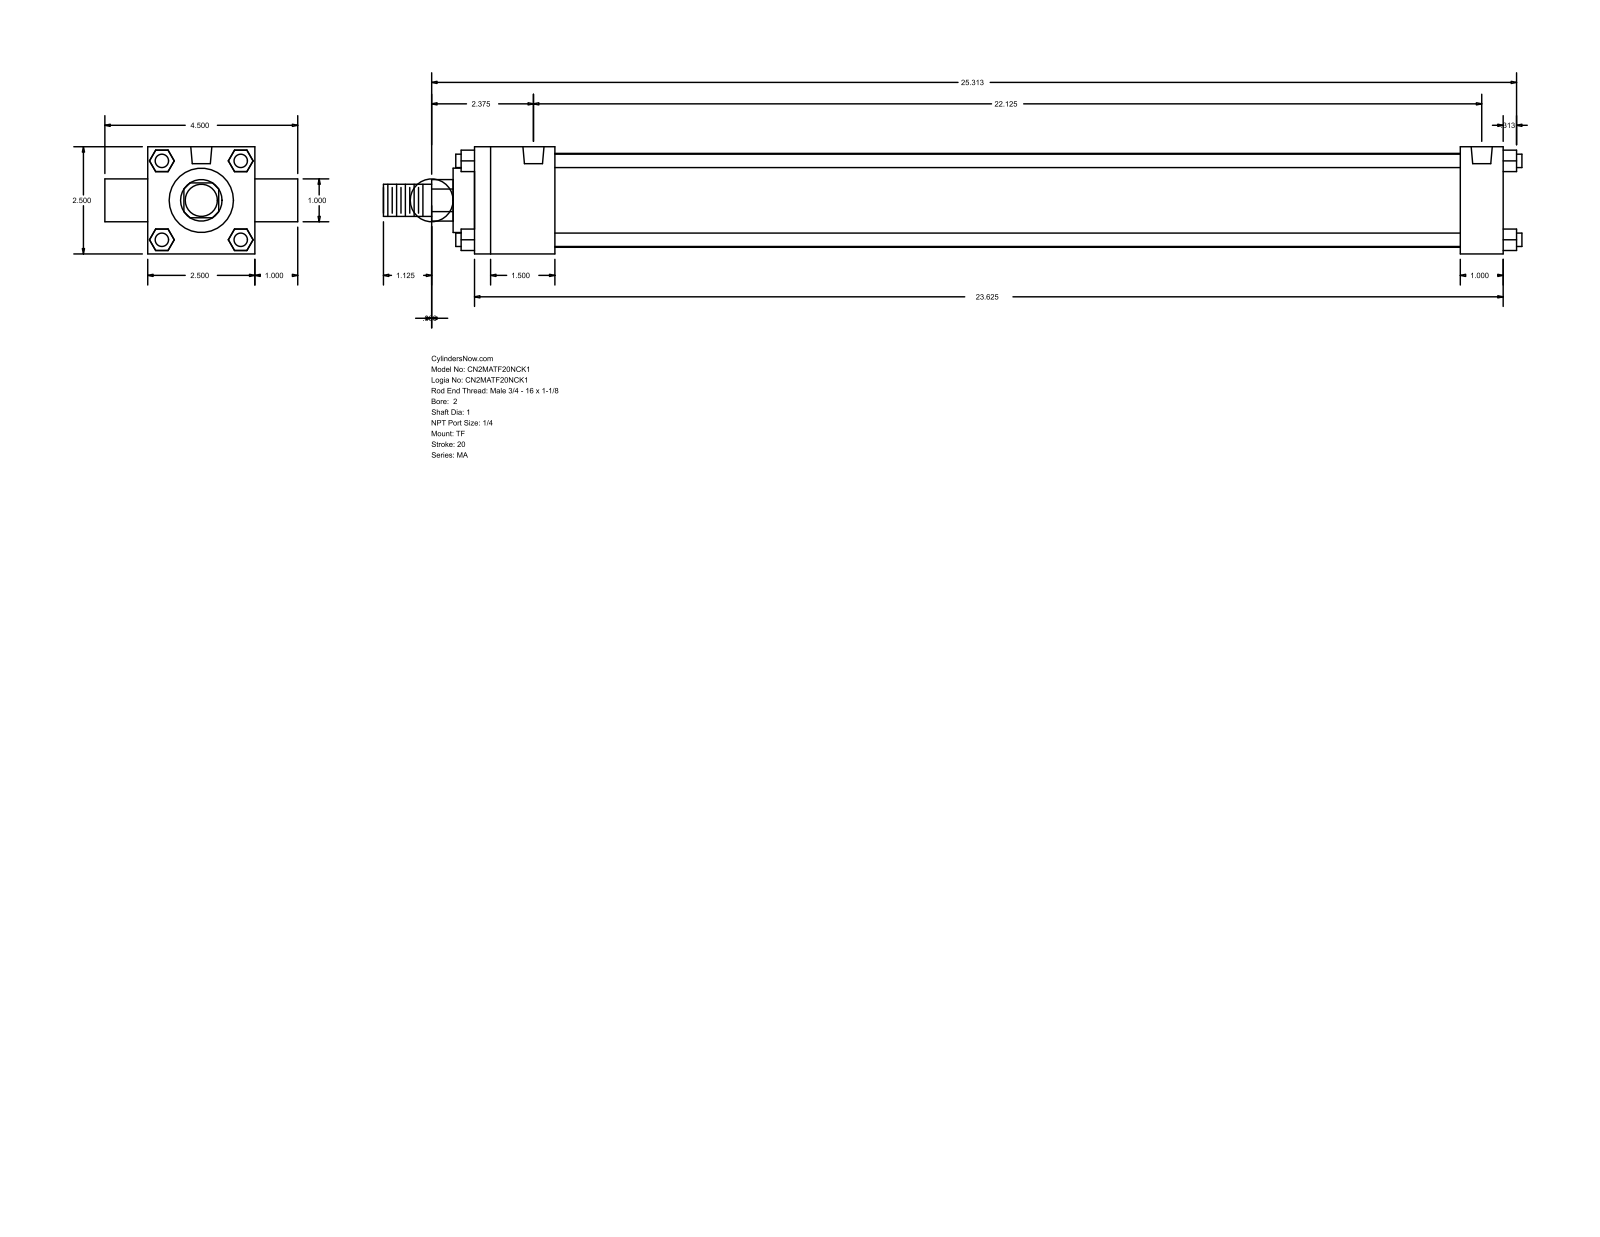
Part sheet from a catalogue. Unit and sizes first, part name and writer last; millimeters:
Units: millimetres
Overall size (bounding box): 674.69 × 114.3 × 63.5
Round holes (diameter × count): ⌀7.94 ×3, ⌀12.49 ×2
Round bosses / shafts (diameter × count): ⌀7.94 ×4, ⌀25.4 ×2, ⌀55.63 ×1, ⌀38.1 ×1, ⌀19.05 ×1
Partial cylindrical surfaces — rounded edges, fillets, slot ends (radius × count): R12.29 ×1
Main face-to-face distances: 63.5, 25.4, 609.6, 12.7, 47.63, 584.2, 536.57, 561.97, 88.9, 23.37
Hole centre spacings: 561.97
Bodies: 0 solids, 120 faces (92 planar, 28 cylindrical, 0 other)
Part name (STEP PRODUCT): MA_TF__0200_1
STEP written by: GSSL Pune (CONFIG_CONTROL_DESIGN)
